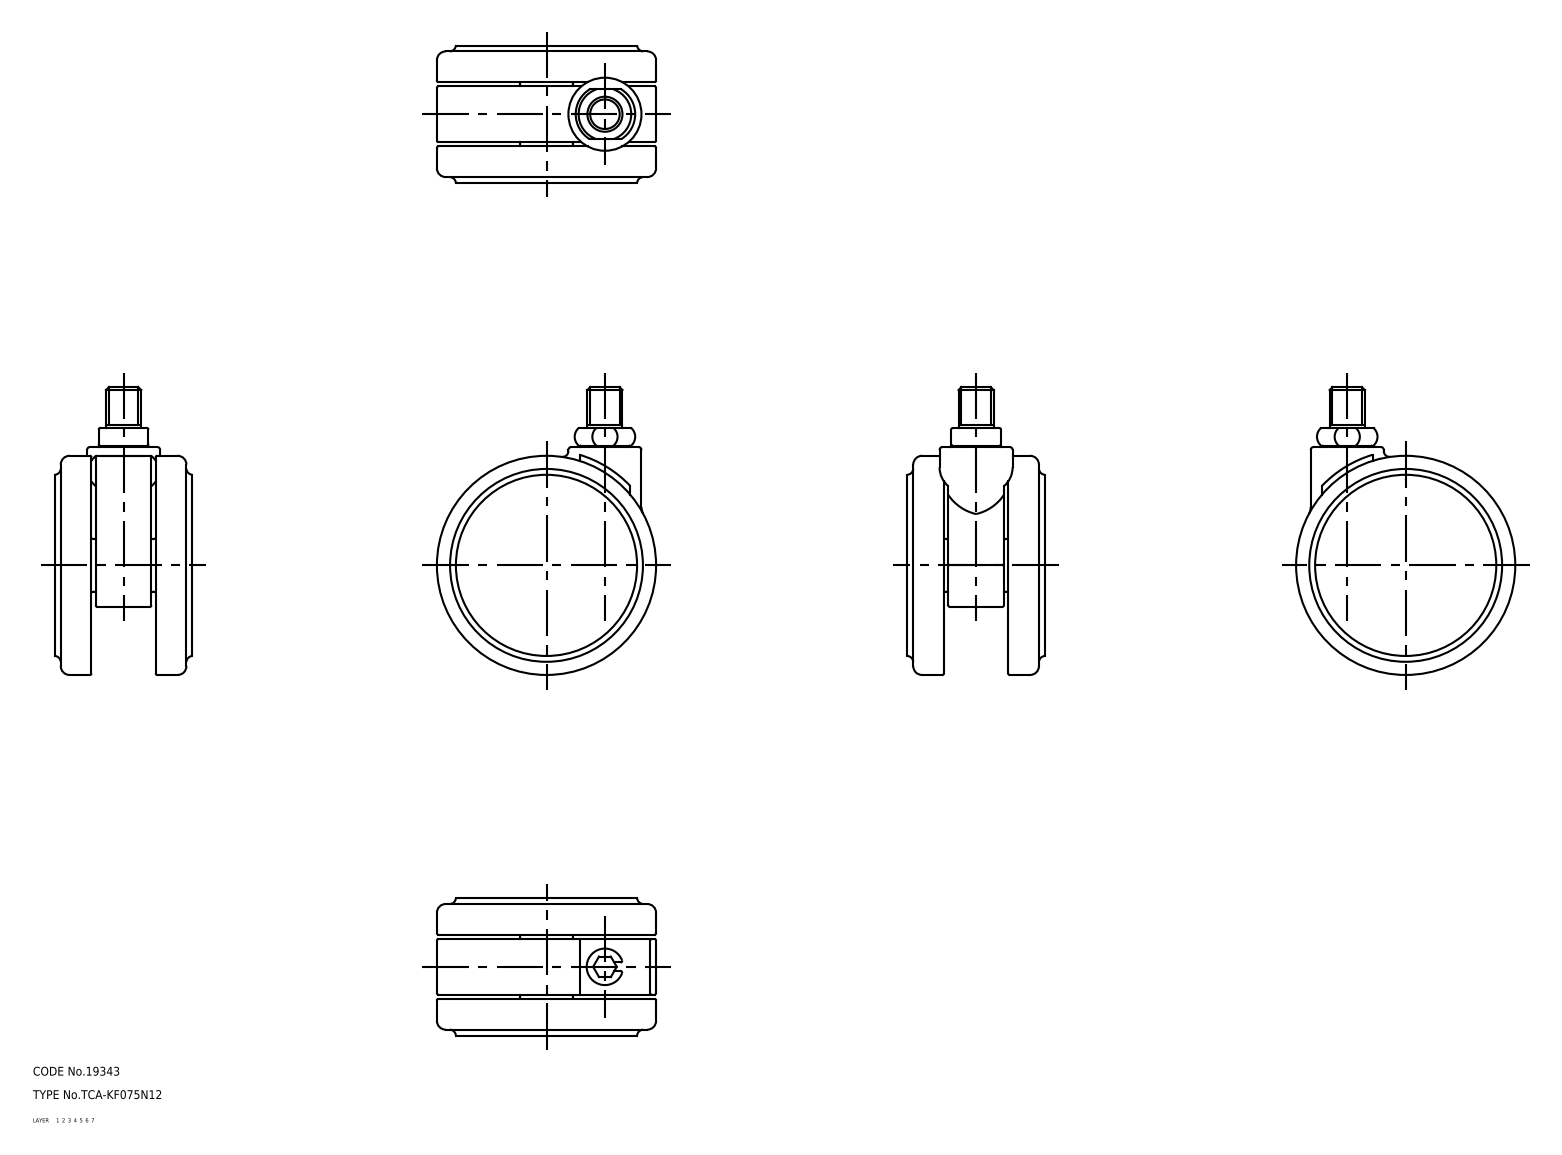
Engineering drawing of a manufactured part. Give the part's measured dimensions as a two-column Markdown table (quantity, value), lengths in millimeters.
| quantity | value |
| --- | --- |
| part name | wheel_mr; TCA_KF075N12; main shaft; wheel |
| STEP written by | SolidWorks 2015 (AUTOMOTIVE_DESIGN) |
| units | millimeters |
| bodies | 4 solids, 126 faces (35 planar, 45 cylindrical, 46 other) |
| overall size | 98.5 × 75 × 47 |
| volume | 160 300 mm³ |
| surface area | 36 969 mm² |
| round holes (diameter × count) | 6 × 1, 43 × 1 |
| round bosses / shafts (diameter × count) | 75 × 1, 25 × 1, 18 × 1, 17 × 1, 12.5 × 1, 12 × 1 |
| partial cylindrical surfaces (radius × count) | 0.5 × 13, 1 × 1, 2.89 × 1, 14.41 × 1, 39.5 × 1 |
| main face-to-face distances | 14, 33, 20.5, 1.5, 12.5, 34.5, 47, 19, 22, 25 |
